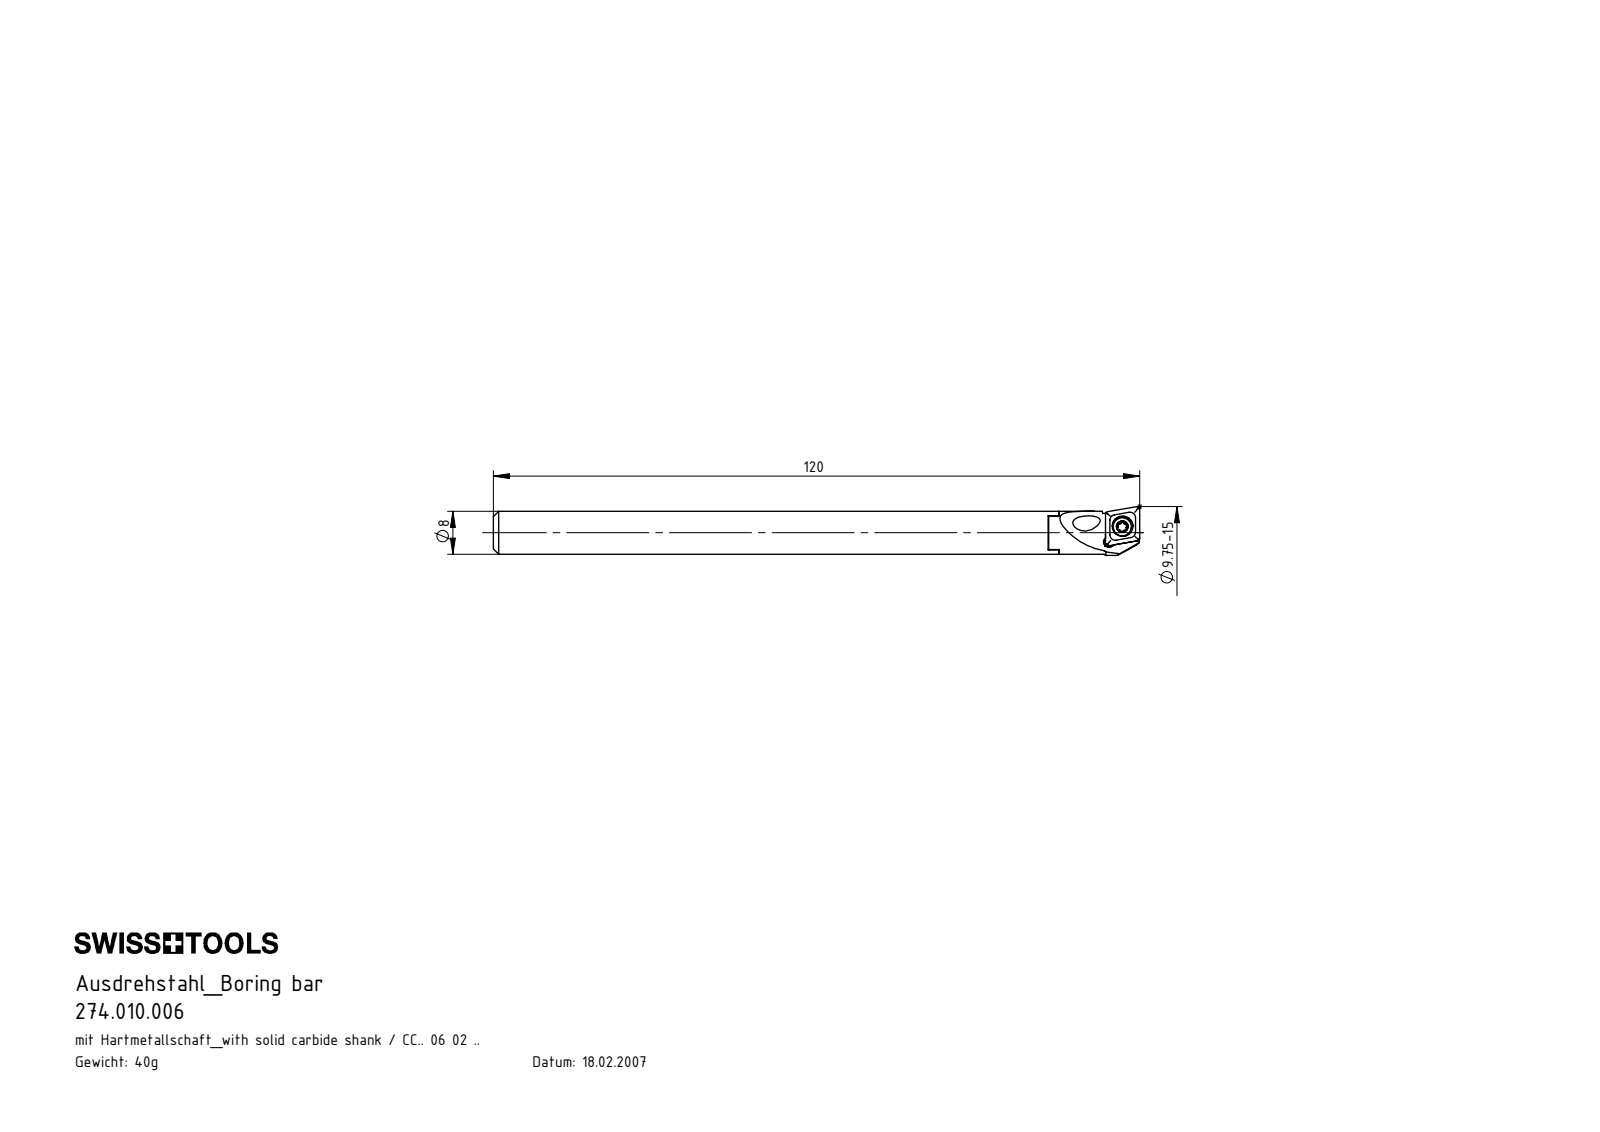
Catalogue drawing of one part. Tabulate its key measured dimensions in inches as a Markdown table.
| quantity | value |
| --- | --- |
| part name | B10.WCA.K13.120; CCMT060204; WCA-ER2.001.005_A; B10-WCA.K13.120_A (+2 more) |
| STEP written by | SolidWorks 2012 (CONFIG_CONTROL_DESIGN) |
| units | inches |
| bodies | 4 solids, 134 faces (43 planar, 40 cylindrical, 51 other) |
| overall size | 4.724 × 0.357 × 0.332 |
| volume | 0.306 in³ |
| surface area | 6.845 in² |
| round holes (diameter × count) | 0.118 × 2, 0.079 × 1, 0.081 × 1, 0.11 × 1, 0.13 × 1, 0.152 × 1 |
| round bosses / shafts (diameter × count) | 0.315 × 1, 0.134 × 1, 0.098 × 1 |
| partial cylindrical surfaces (radius × count) | 0.008 × 6, 0.014 × 5, 0.014 × 1, 0.165 × 1, 0.177 × 1, 0.394 × 1 |
| main face-to-face distances | 0.077, 0.194, 4.132, 4.136, 4.055, 0.081, 4.059, 0.073, 0.191, 0.198 |
| hole center spacings | 0.154, 0.158 |
